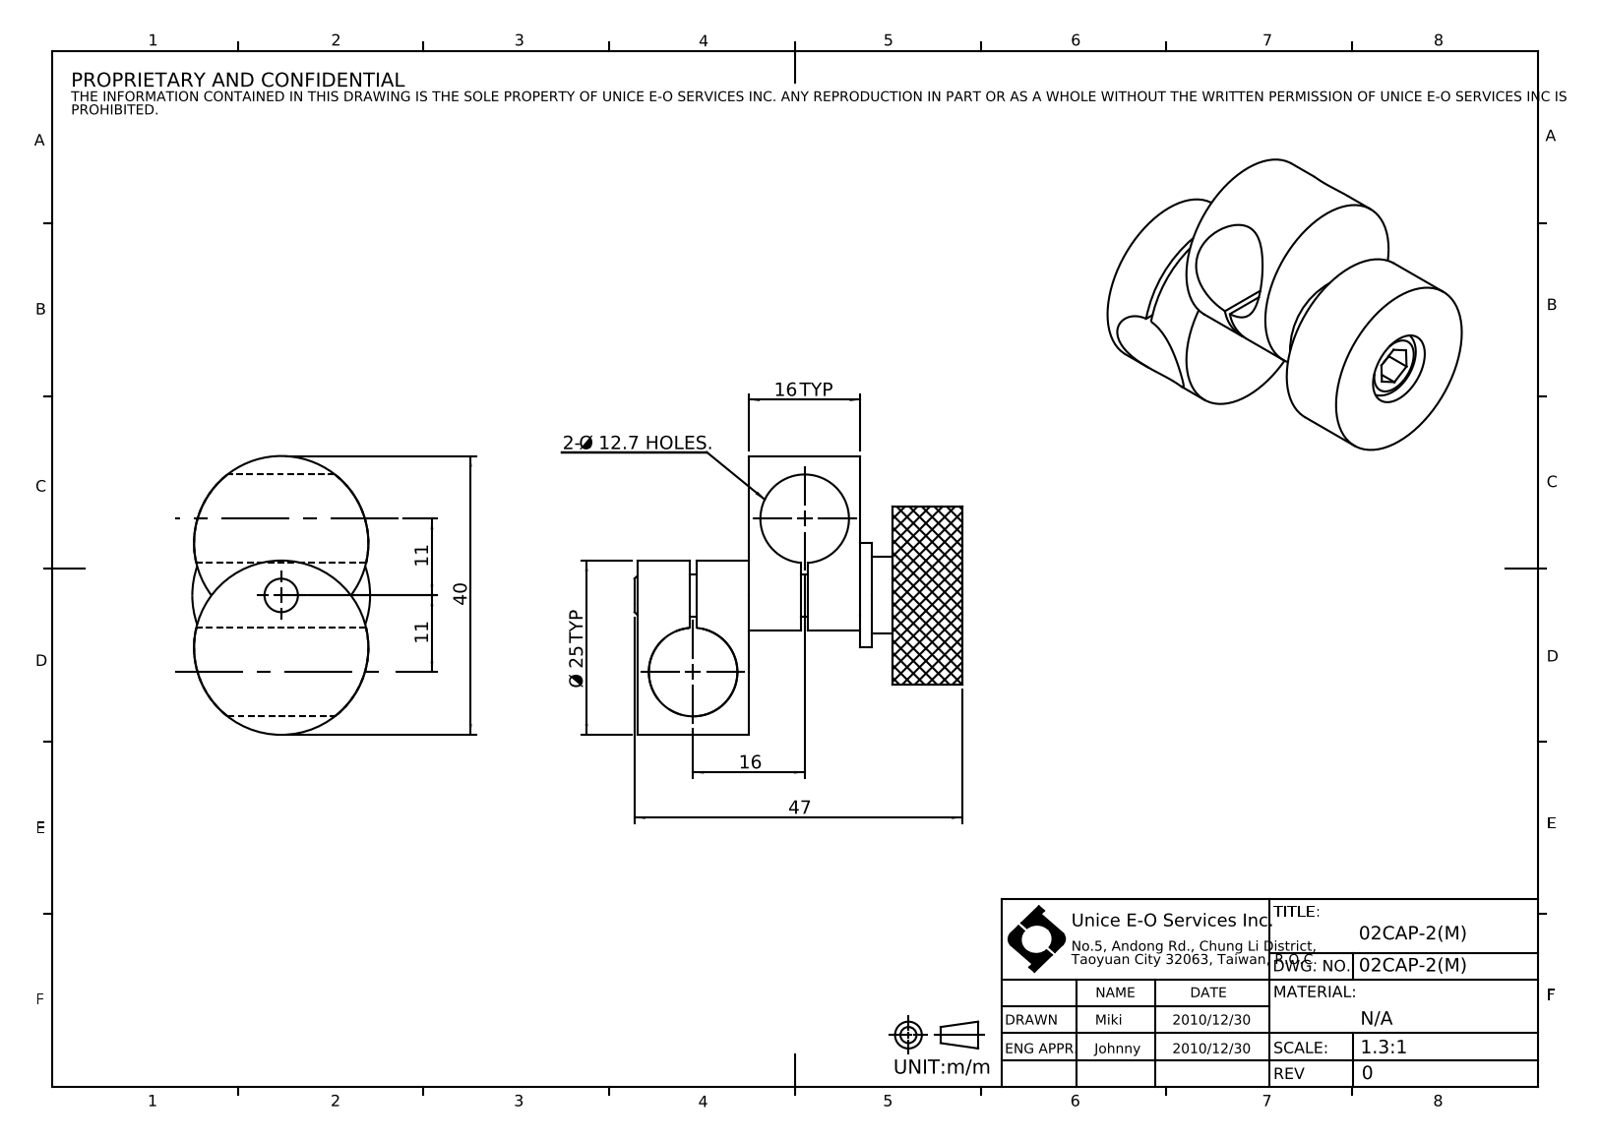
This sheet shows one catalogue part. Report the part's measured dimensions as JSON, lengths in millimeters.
{"part_name": "02CAP-2(M)", "step_written_by": "SolidWorks 2016 (CONFIG_CONTROL_DESIGN)", "units": "millimeters", "bodies": {"solids": 5, "faces": 67, "planar": 23, "cylindrical": 36, "other": 8}, "overall_size": [47, 40, 25.5], "volume_mm3": 15036, "surface_area_mm2": 10346, "round_holes": [[12.7, 2], [5, 1], [6.5, 1], [10.5, 1]], "round_bosses_or_shafts": [[25, 2], [25.5, 1], [15, 1], [11, 1], [10, 1], [6, 1]], "face_to_face_distances": [16, 7.5, 8.5, 32, 46.6, 30.6, 14.6, 36.6, 20.6, 4.6], "hole_center_spacings": [27.2]}
